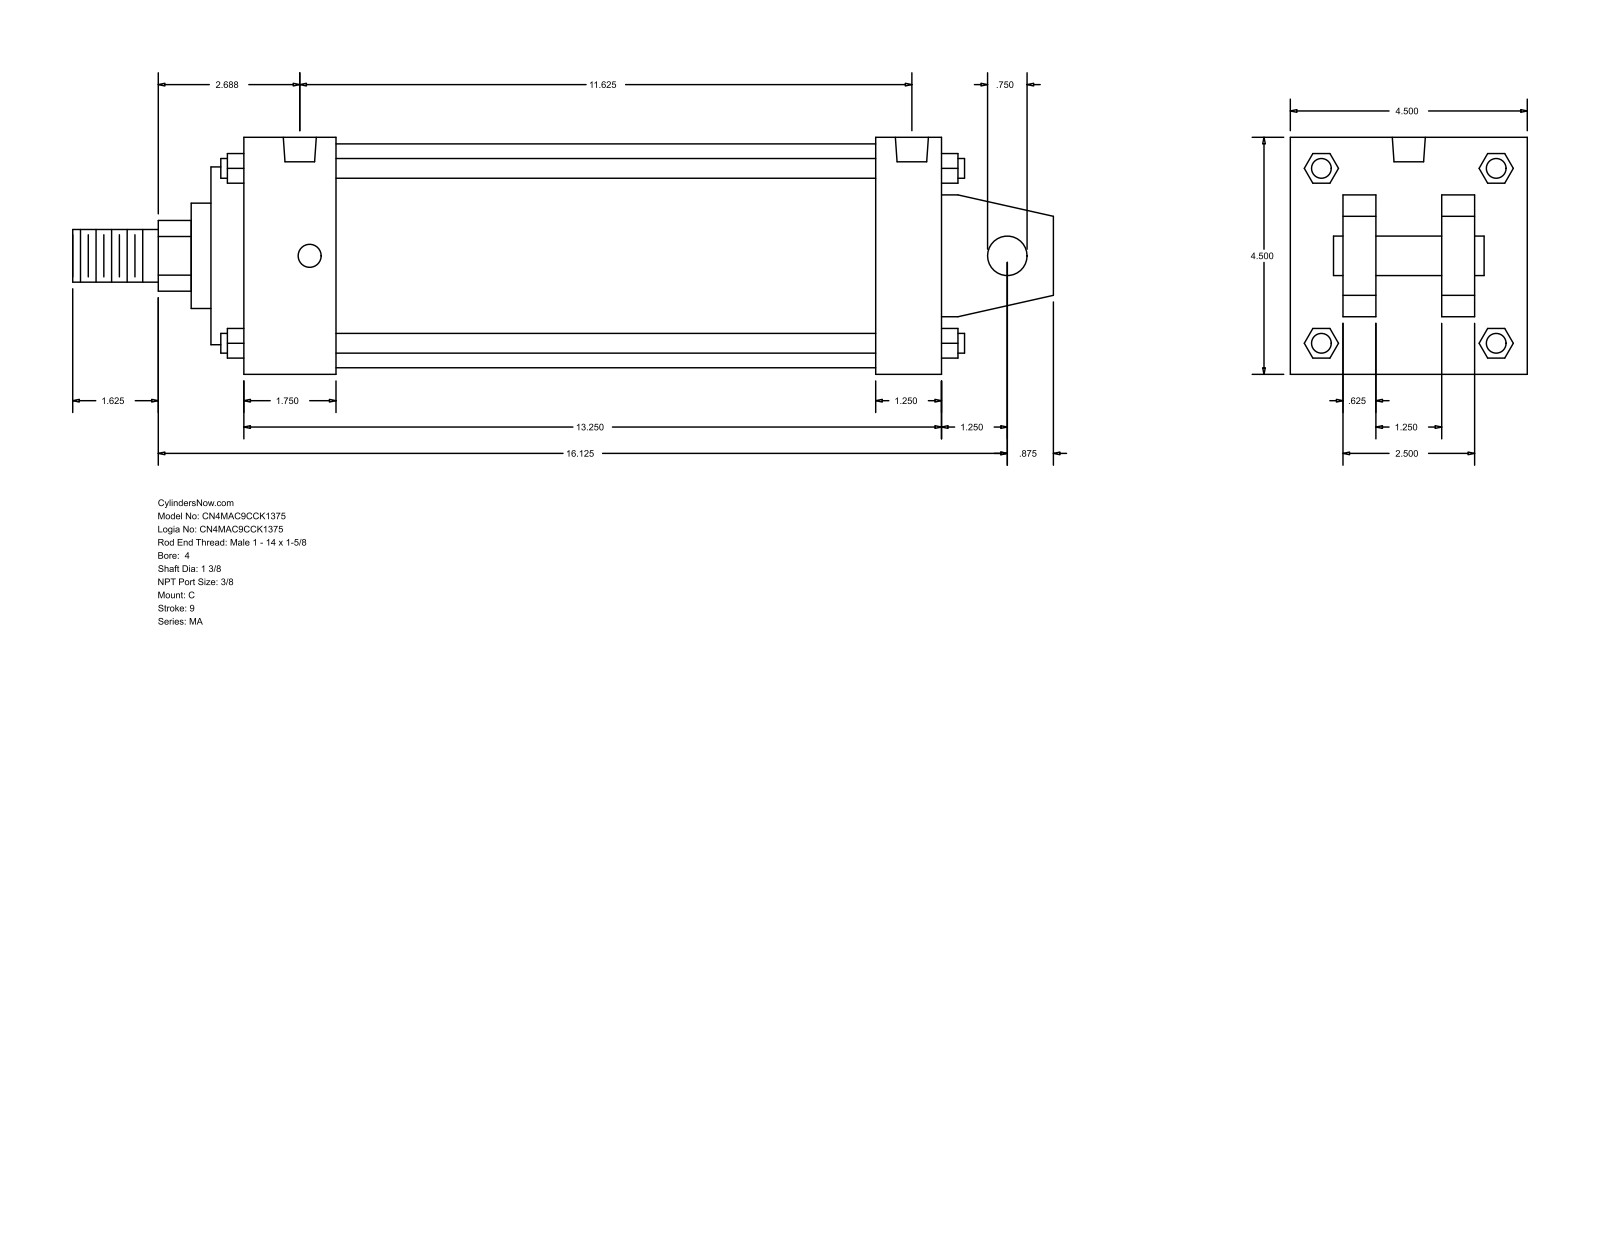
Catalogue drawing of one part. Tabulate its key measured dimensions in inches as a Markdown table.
| quantity | value |
| --- | --- |
| part name | MA_C__0400_1.375 |
| STEP written by | GSSL Pune (CONFIG_CONTROL_DESIGN) |
| units | inches |
| bodies | 0 solids, 141 faces (109 planar, 32 cylindrical, 0 other) |
| overall size | 18.625 × 4.5 × 4.5 |
| round holes (diameter × count) | 0.437 × 4, 0.627 × 2 |
| round bosses / shafts (diameter × count) | 0.375 × 4, 4.25 × 1, 3.375 × 1, 2 × 1, 1.375 × 1, 1 × 1, 0.75 × 1 |
| partial cylindrical surfaces (radius × count) | 0.672 × 1 |
| main face-to-face distances | 4.5, 0.625, 13.25, 2.875, 1.625, 1, 3.5, 1.875, 13.875, 12.625 |
| hole center spacings | 0.188, 11.25, 11.437, 11.625 |
